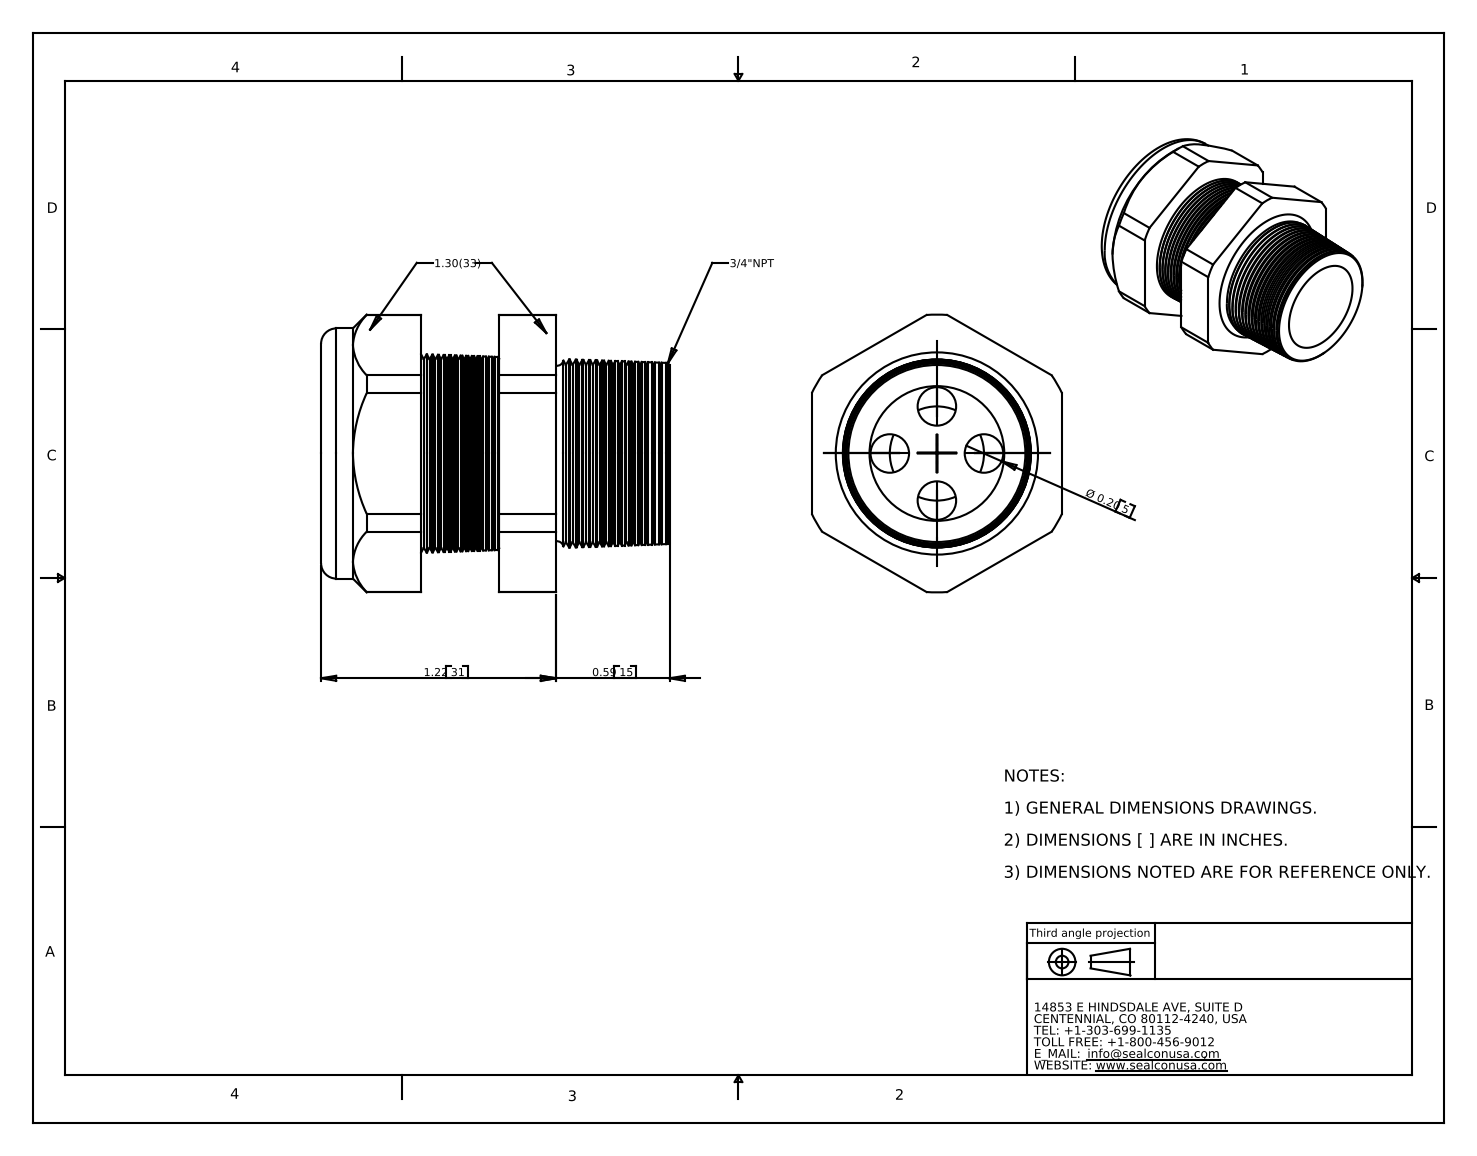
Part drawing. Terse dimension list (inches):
name: CD21N6-GY
written by: SolidWorks 2007 (CONFIG_CONTROL_DESIGN)
unit: in
bodies: 2 solids, 236 faces (20 planar, 28 cylindrical, 188 other)
size: 1.77 × 1.443 × 1.3
volume: 1.249 in³; area: 17.92 in²
holes: 4× ⌀0.2, 1× ⌀0.69, 1× ⌀0.71
bosses: 1× ⌀1.3
rounds: 1× R0.721
face distances: 1.3, 0.925, 0.52, 0.405, 1.22, 0.7, 0.295, 1.77, 1.25, 0.845
hole spacings: 0.244, 0.346, 0.489
